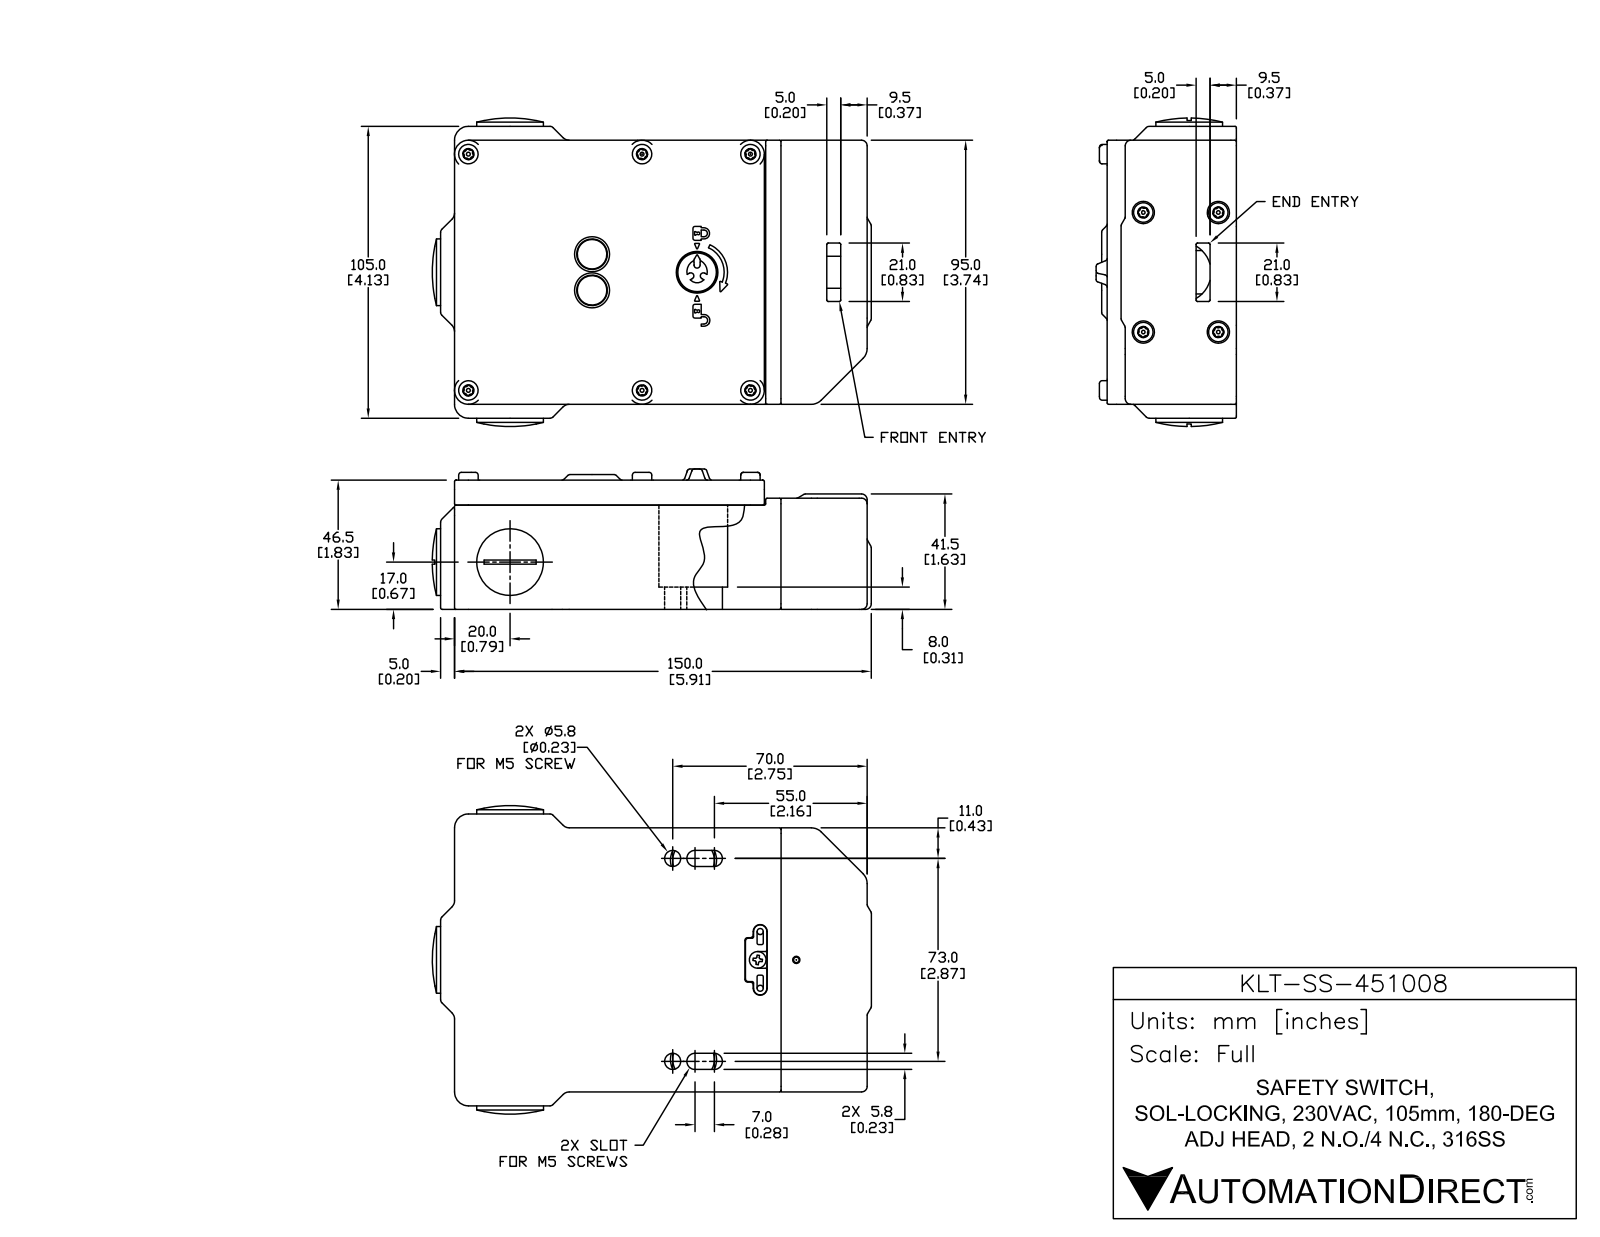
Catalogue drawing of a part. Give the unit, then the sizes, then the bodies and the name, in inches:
Units: inches
Overall size (bounding box): 6.22 × 4.37 × 1.988
Round holes (diameter × count): ⌀0.13 ×10, ⌀0.157 ×10, ⌀0.098 ×8, ⌀0.177 ×6, ⌀0.185 ×6, ⌀0.165 ×4, ⌀0.197 ×4, ⌀0.315 ×4, ⌀0.591 ×3, ⌀0.087 ×2, ⌀0.217 ×2, ⌀0.228 ×2
Round bosses / shafts (diameter × count): ⌀0.276 ×10, ⌀0.138 ×10, ⌀0.055 ×6, ⌀0.236 ×5, ⌀0.051 ×4, ⌀0.709 ×3, ⌀0.945 ×2, ⌀0.449 ×2
Partial cylindrical surfaces — rounded edges, fillets, slot ends (radius × count): R0.02 ×451, R0.039 ×162, R0.012 ×54, R0.079 ×21, R0.006 ×14, R0.008 ×14, R0.197 ×10, R0.031 ×8
Main face-to-face distances: 0.118, 0.087, 1.831, 0.134, 1.744, 0.098, 0.138, 3.606, 0.256, 1.476
Hole centre spacings: 1, 2.606, 1.648, 3.346, 0.187, 0.296, 0.383, 0.396
Volume: 14 in³ · Surface area: 209.2 in²
Bodies: 21 solids, 3390 faces (741 planar, 1370 cylindrical, 1279 other)
Part name (STEP PRODUCT): KLT-SS-451008
STEP written by: SolidWorks 2017 (AUTOMOTIVE_DESIGN)
